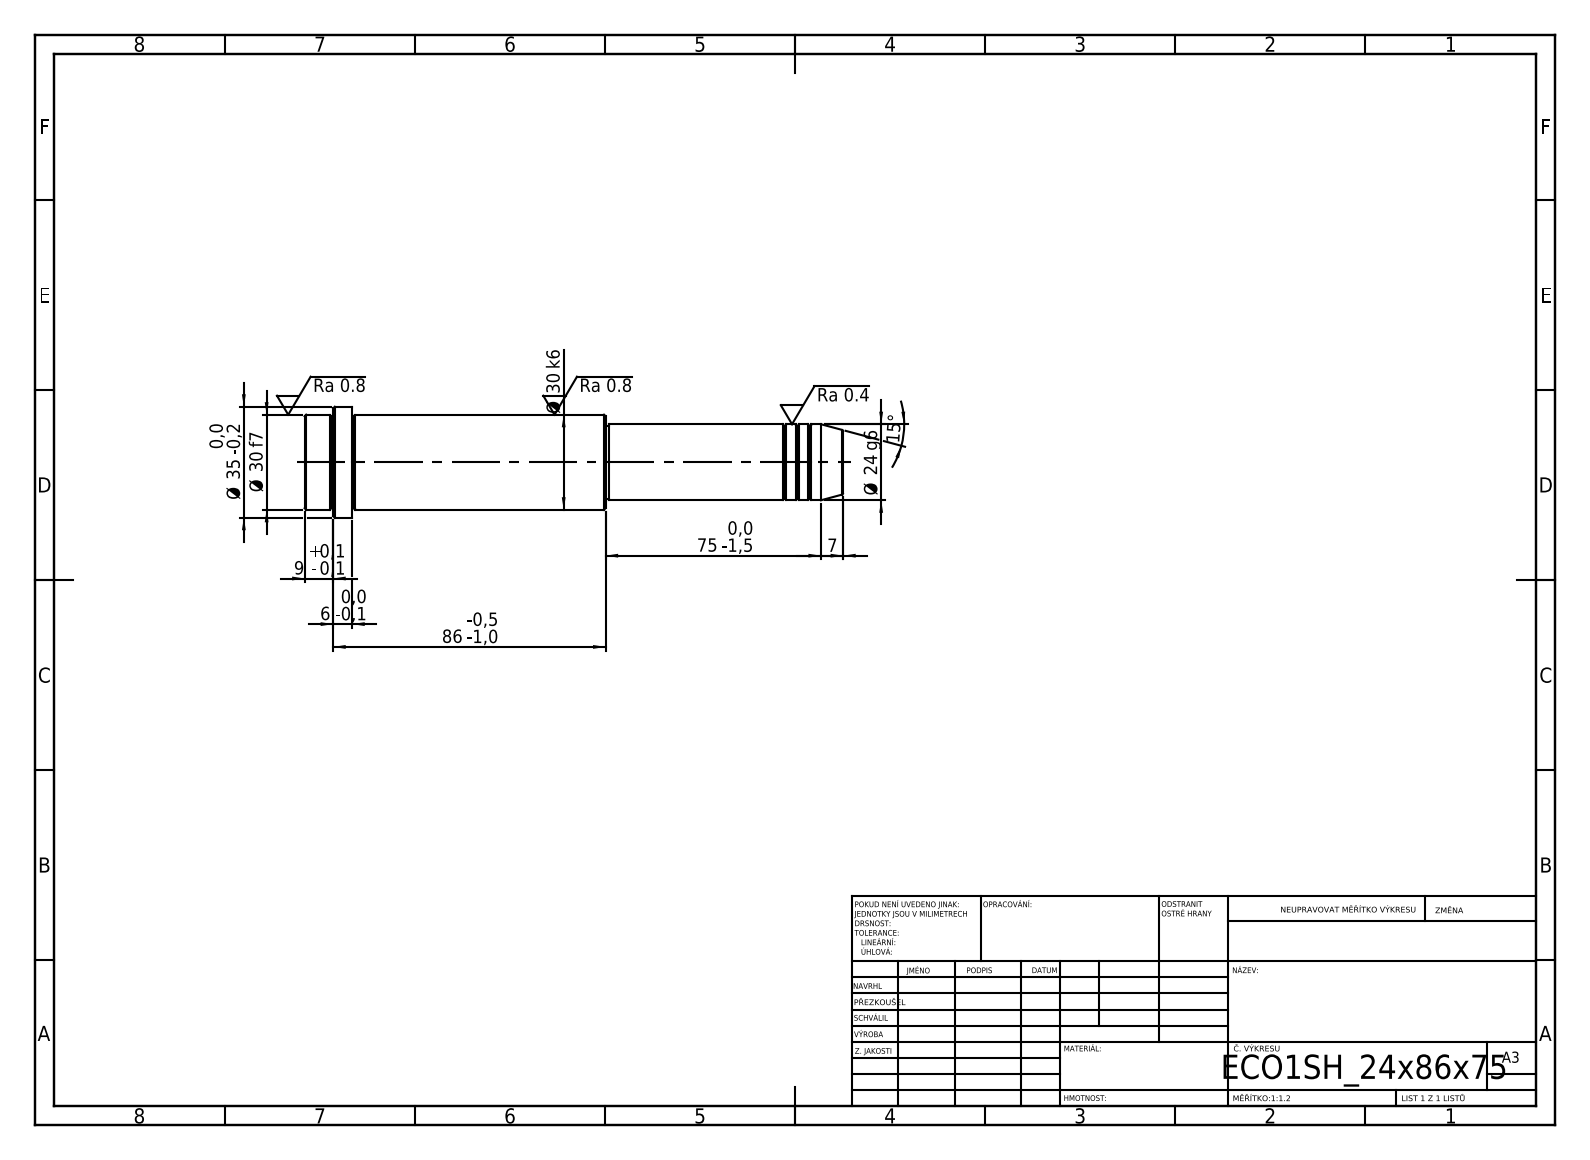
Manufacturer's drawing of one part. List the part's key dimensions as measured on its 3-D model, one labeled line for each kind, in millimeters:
STEP written by: SolidWorks 2019 (CONFIG_CONTROL_DESIGN)
Units: millimetres
Bodies: 1 solid, 52 faces (6 planar, 16 cylindrical, 30 other)
Overall size (bounding box): 170 × 35 × 35
Volume: 101 907 mm³ · Surface area: 16 668 mm²
Round bosses / shafts (diameter × count): ⌀35 ×1, ⌀30 ×1, ⌀24 ×1, ⌀23 ×1
Main face-to-face distances: 170, 155, 15, 75, 80, 95, 161, 86, 6, 9
